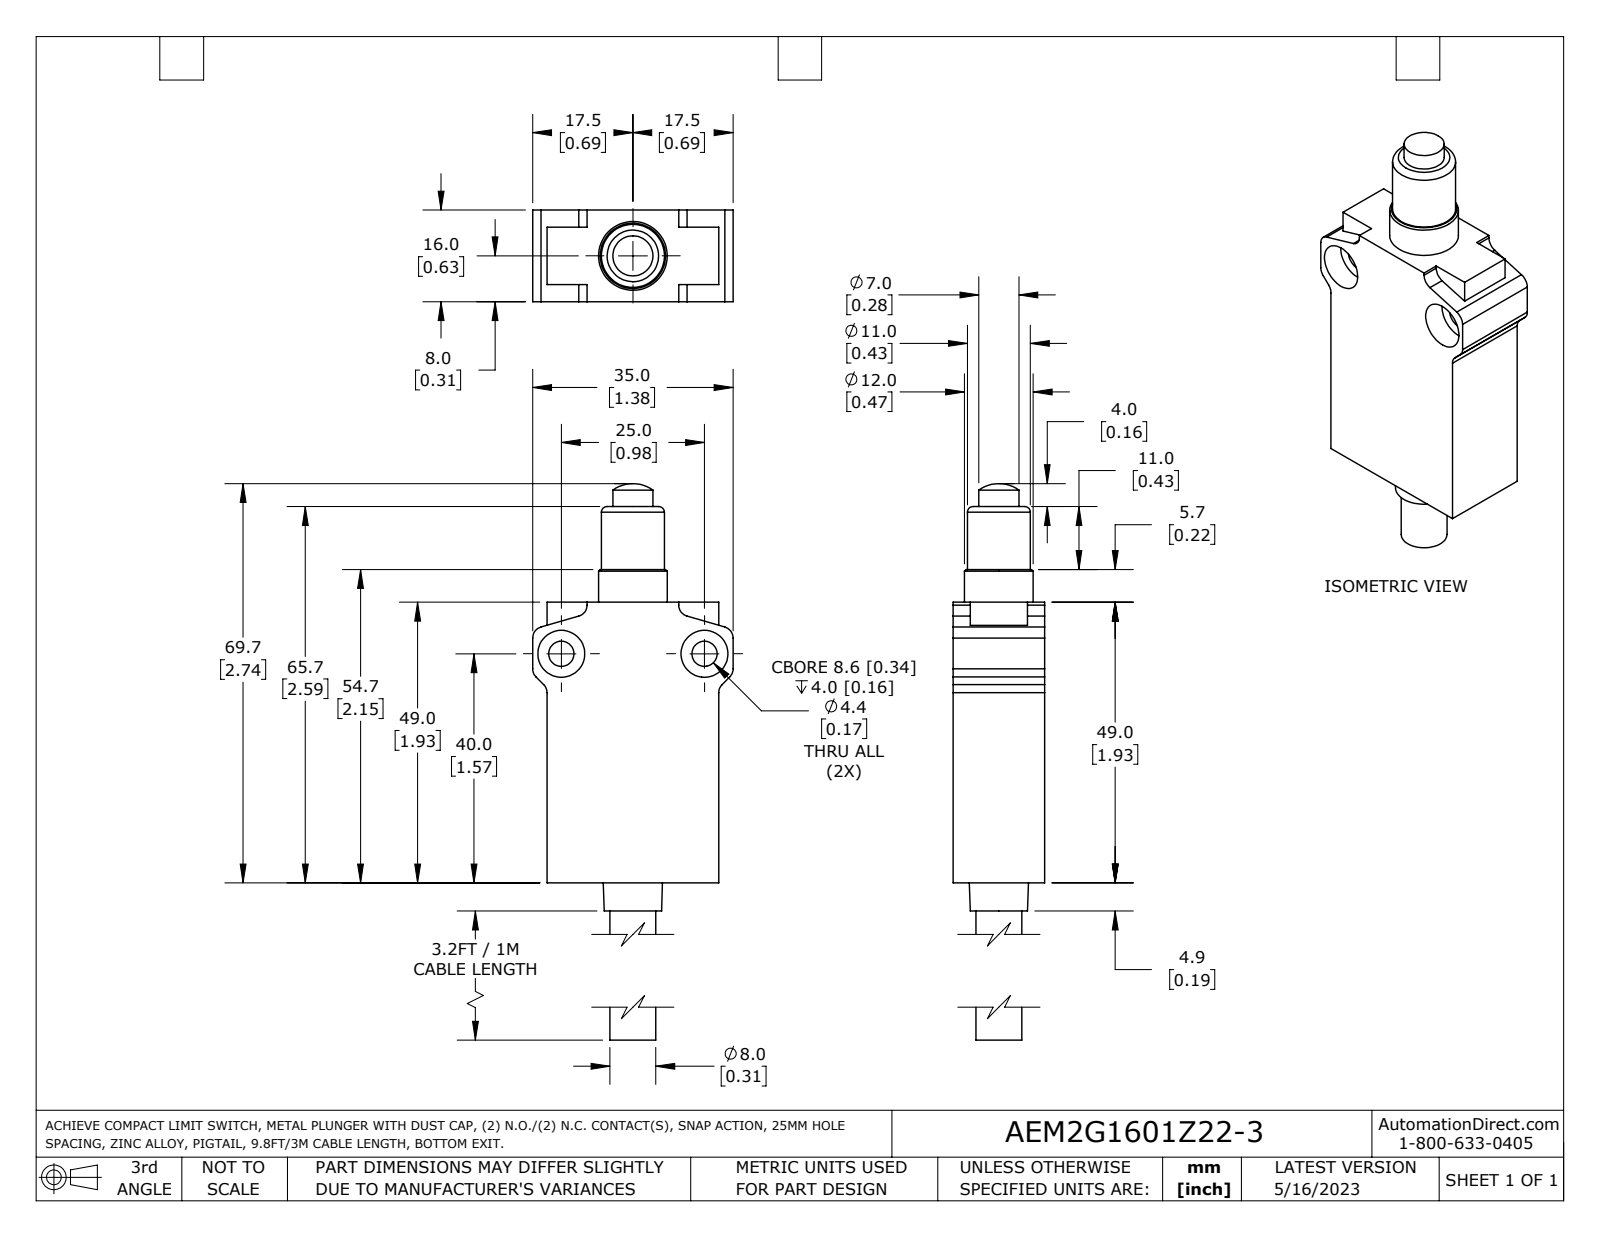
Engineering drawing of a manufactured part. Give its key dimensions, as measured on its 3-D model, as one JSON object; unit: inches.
{"part_name": "AEM2G1601Z22-3", "step_written_by": "SolidWorks 2021 (AUTOMOTIVE_DESIGN)", "units": "inches", "bodies": {"solids": 1, "faces": 81, "planar": 46, "cylindrical": 27, "other": 8}, "overall_size": [3.331, 1.378, 0.63], "volume_in3": 1.551, "surface_area_in2": 12.62, "round_holes": [[0.173, 2], [0.323, 2], [0.28, 1]], "round_bosses_or_shafts": [[0.472, 1], [0.433, 1], [0.315, 1], [0.276, 1], [0.197, 1]], "partial_cylinders_radius": [[0.079, 8], [0.256, 1]], "face_to_face_distances": [0.63, 1.181, 1.929, 0.098, 1.28, 0.472, 0.157, 0.039, 1.378, 0.118], "hole_center_spacings": [0.984]}
